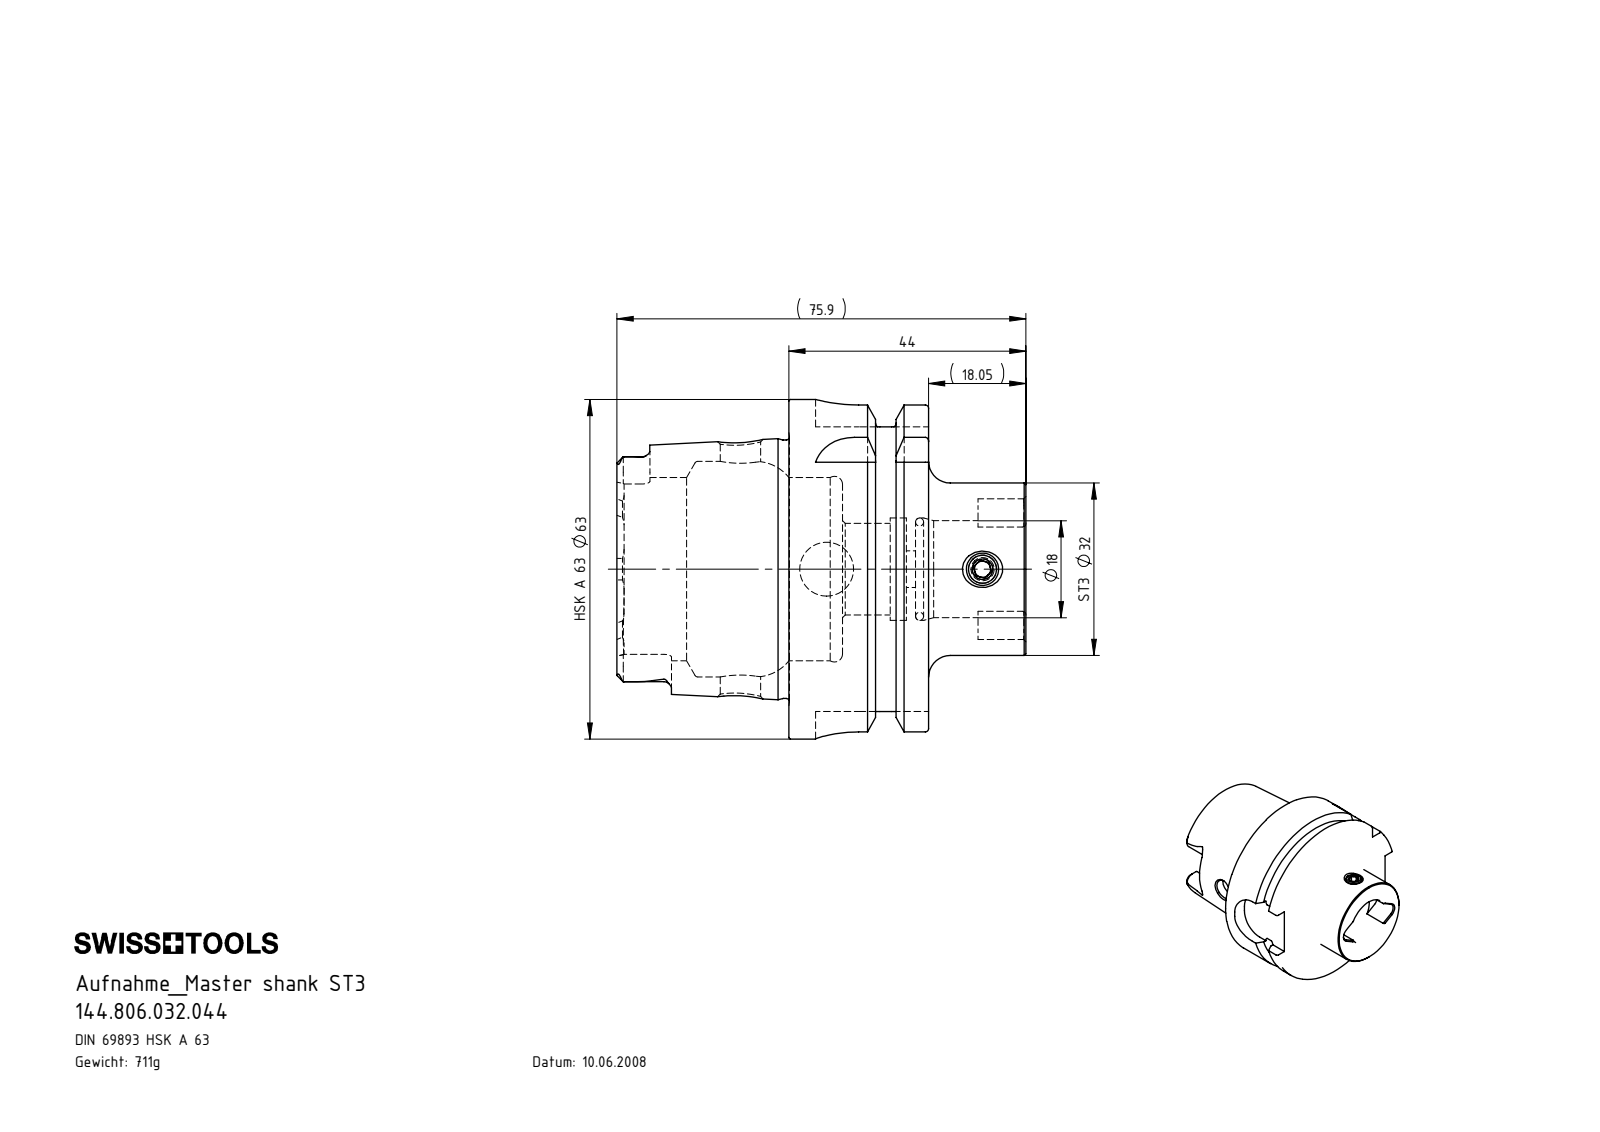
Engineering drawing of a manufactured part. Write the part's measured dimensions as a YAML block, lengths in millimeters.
part_name: "DIN 3771 - 16x1.5; ST3-ER1.001.008_A; HA6-ST3.K01.044_B_Fertigbearbeitung; 144.806.032.044"
step_written_by: "SolidWorks 2017 (CONFIG_CONTROL_DESIGN)"
units: millimeters
bodies: {solids: 3, faces: 227, planar: 69, cylindrical: 58, other: 100}
overall_size: [75.9, 63, 63]
volume: 90689
surface_area: 25624
round_holes:
  - {diameter: 3, count: 1}
  - {diameter: 5.25, count: 1}
  - {diameter: 6.8, count: 1}
  - {diameter: 7.5, count: 1}
  - {diameter: 10, count: 1}
  - {diameter: 17, count: 1}
  - {diameter: 18, count: 1}
  - {diameter: 19, count: 1}
  - {diameter: 34, count: 1}
  - {diameter: 40, count: 1}
round_bosses_or_shafts:
  - {diameter: 63, count: 1}
  - {diameter: 54.95, count: 1}
  - {diameter: 47.94, count: 1}
  - {diameter: 32, count: 1}
  - {diameter: 6, count: 1}
partial_cylinders:
  - {radius: 1.4, count: 6}
  - {radius: 2.88, count: 4}
  - {radius: 8, count: 4}
  - {radius: 2.5, count: 2}
face_to_face_distances: [25.95, 16, 9.95, 44, 34.05, 18.05, 31.9, 41.85, 57.85, 75.9]
hole_center_spacings: [28.95]
